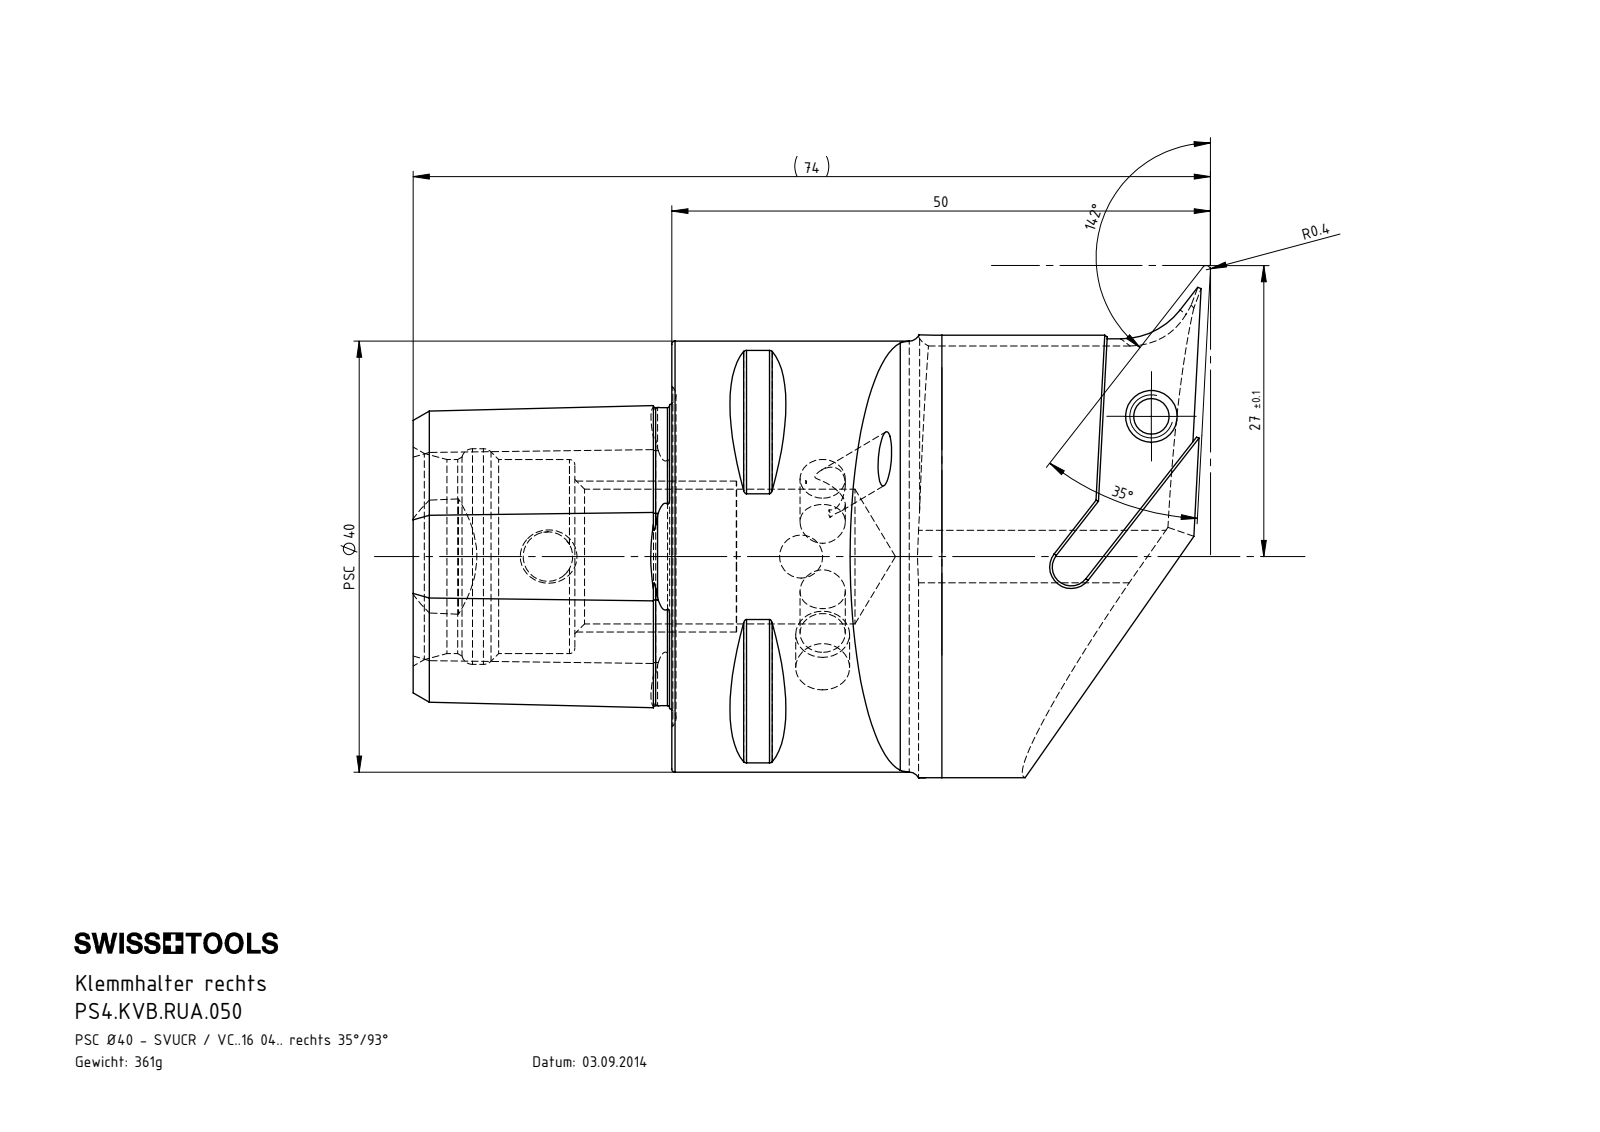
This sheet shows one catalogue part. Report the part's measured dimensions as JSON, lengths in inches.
{"part_name": "PS4.KVB.RUA.050; PS4-KVB.RUA.050_A_Fertigbearbeitung; VCMT160404; WCB-ER2.001.009_A (+1 more)", "step_written_by": "SolidWorks 2017 (AUTOMOTIVE_DESIGN)", "units": "inches", "bodies": {"solids": 5, "faces": 215, "planar": 55, "cylindrical": 47, "other": 113}, "overall_size": [2.913, 1.87, 1.589], "volume_in3": 2.846, "surface_area_in2": 20.37, "round_holes": [[0.157, 2], [0.165, 2], [0.13, 1], [0.173, 1], [0.181, 1], [0.197, 1], [0.24, 1], [0.492, 1], [0.709, 1], [0.787, 1]], "round_bosses_or_shafts": [[1.575, 1], [0.207, 1], [0.197, 1], [0.157, 1]], "partial_cylinders_radius": [[0.012, 8], [0.013, 6], [0.023, 6], [0.031, 1], [0.069, 1], [0.276, 1], [0.634, 1], [0.807, 1]], "face_to_face_distances": [0.176, 0.945, 0.611, 0.614, 0.789, 1.39, 0.354, 0.591, 0.801, 0.187], "hole_center_spacings": [0.925, 1.379, 2.264]}
